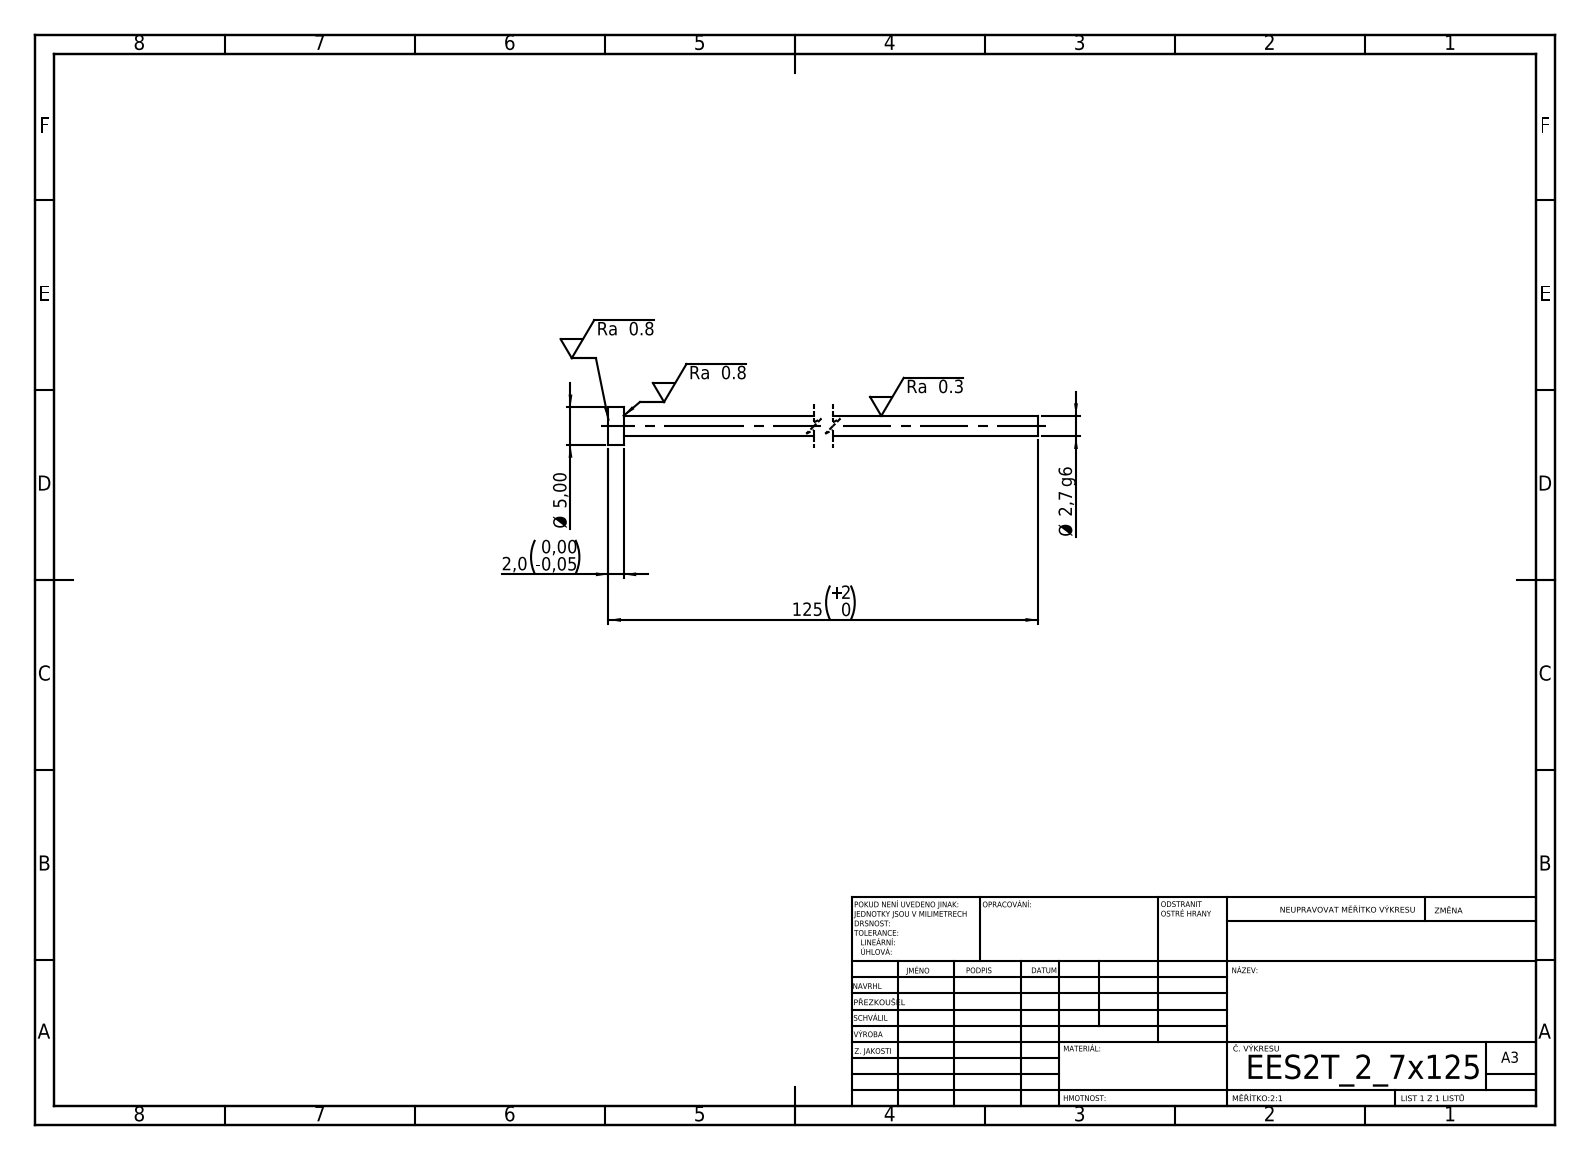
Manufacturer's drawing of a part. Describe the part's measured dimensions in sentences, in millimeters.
Its 3-D file was written by "SolidWorks 2019 (CONFIG_CONTROL_DESIGN)". It is 1 solid with 7 faces: 3 planar, 4 cylindrical and 0 other. Overall it measures 125 by 5 by 5 millimeters. Its volume is 744 cubic millimeters and its surface area 1 114 square millimeters. Round bosses or shafts: 1 of diameter 5, 1 of diameter 2.7. The main face-to-face distances are 2, 125, 123.
